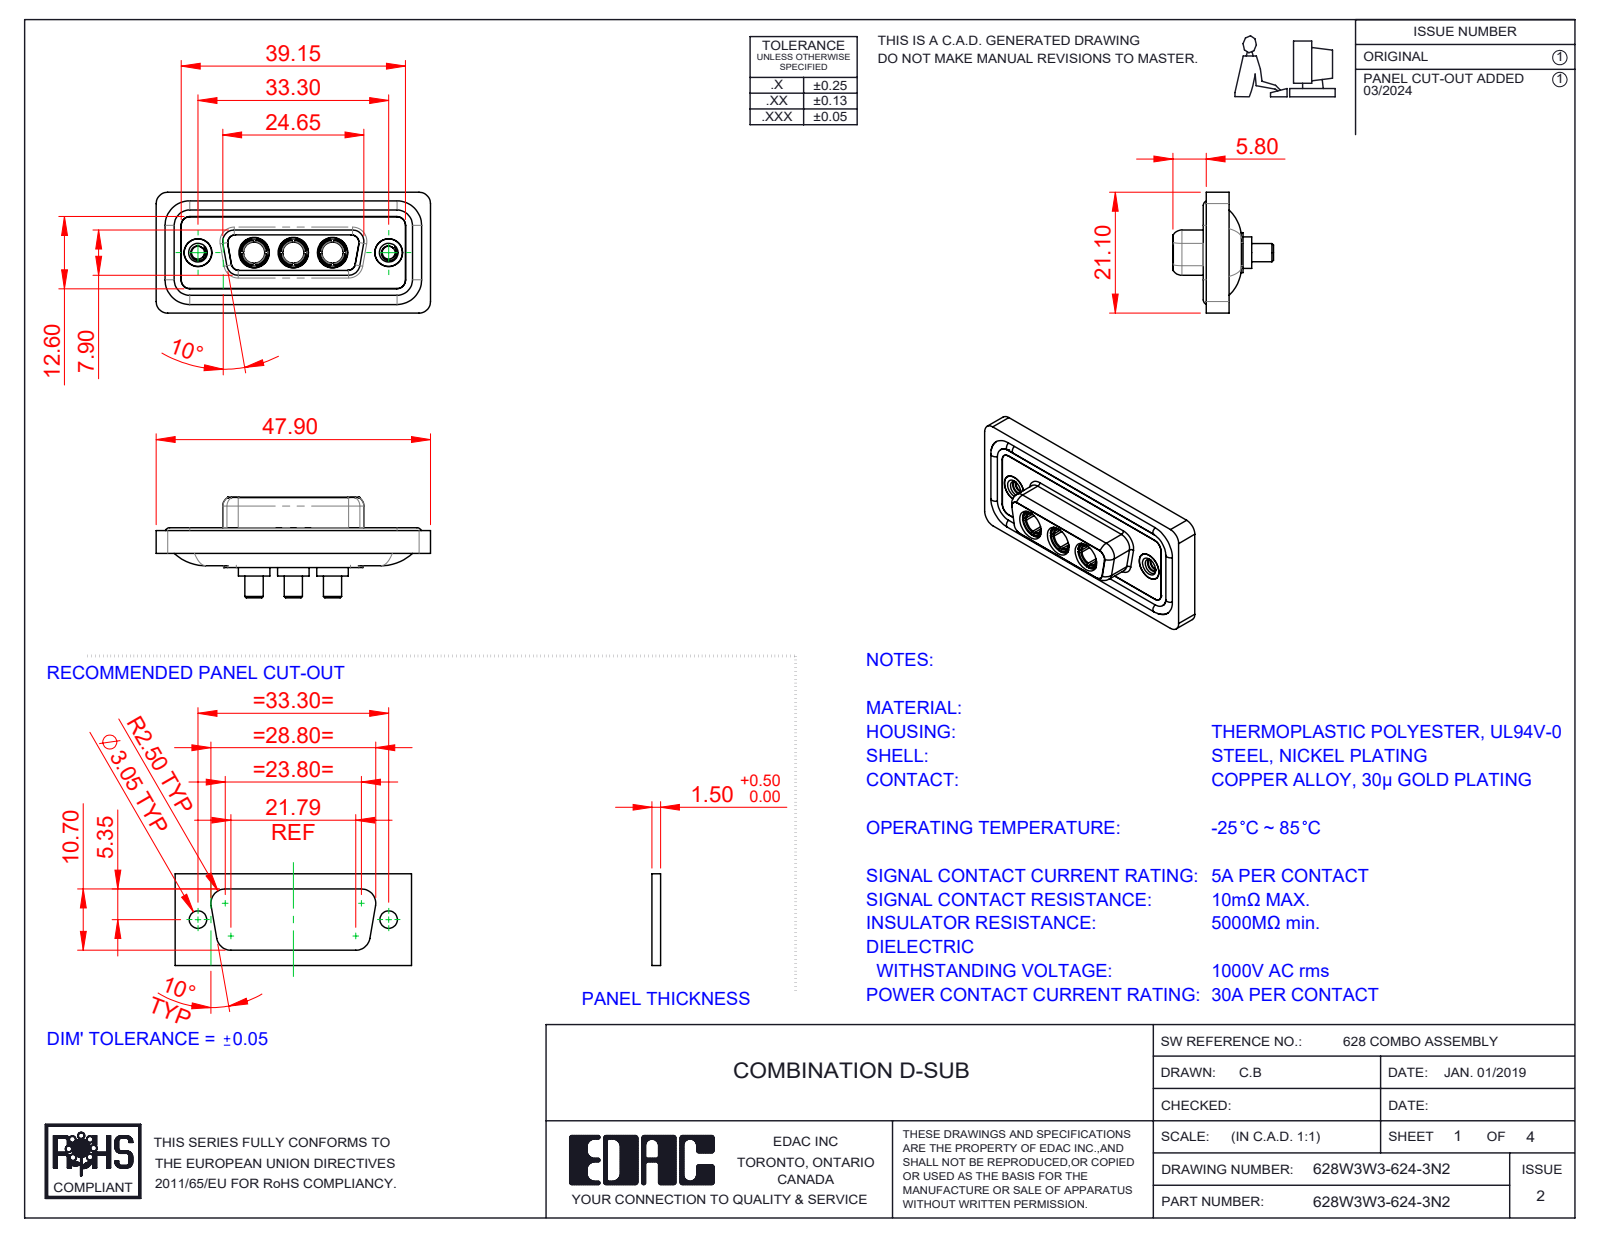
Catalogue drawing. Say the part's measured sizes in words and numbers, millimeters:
The part is named "628Combo Waterproof Housing_15 Contacts; Power Socket_30A S; 628Combo Shell Front_15 Contacts; 628Combo Shell Rear_15 Contacts (+3 more)". Its 3-D file was written by "SolidWorks 2023 (CONFIG_CONTROL_DESIGN)". It is 13 solids with 608 faces: 192 planar, 257 cylindrical and 159 other. Overall it measures 47.9 by 21.1 by 17.55 millimeters. Its volume is 6 048 cubic millimeters and its surface area 9 752 square millimeters. Round holes: 5 of diameter 4.85, 3 of diameter 3.7, 3 of diameter 5.3, 2 of diameter 2.26, 2 of diameter 4, 2 of diameter 4.05, 2 of diameter 5. Round bosses or shafts: 4 of diameter 1.6, 3 of diameter 5.5, 3 of diameter 5.2, 3 of diameter 4.96, 3 of diameter 4.75, 3 of diameter 3.75, 3 of diameter 3.2, 2 of diameter 4.95. Partial cylindrical surfaces (rounded edges, fillets, slot ends): 22 of radius 1.5, 20 of radius 2, 12 of radius 1.35, 8 of radius 1.6, 4 of radius 0.25, 4 of radius 0.5, 4 of radius 0.6, 4 of radius 0.65. The main face-to-face distances are 0.4, 1.8, 1.6, 0.5, 7.45, 1.1, 2.9, 5.65, 7.05, 6.6. The hole center spacings are 6.85, 9.8, 16.65, 23.5, 13.7, 33.3.
